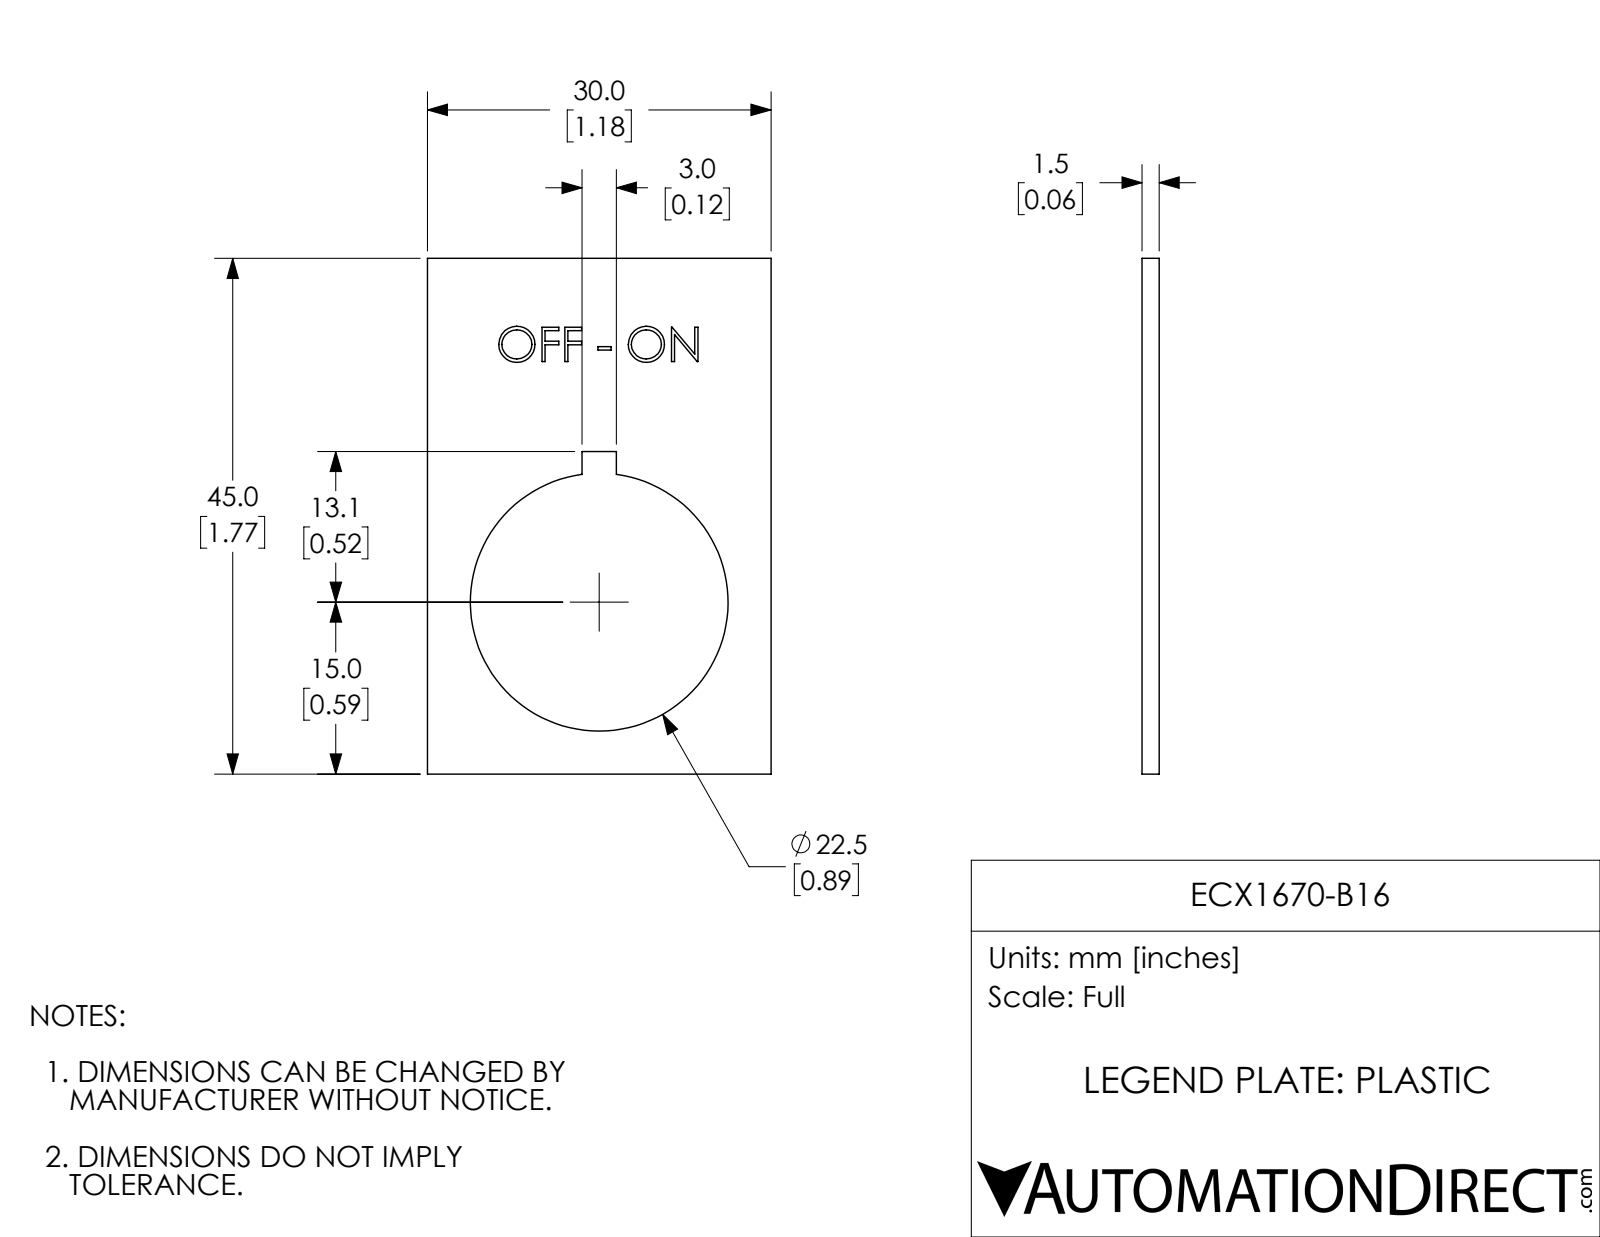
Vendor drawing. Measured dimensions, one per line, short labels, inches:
name: ECX1670-B16
written by: SolidWorks 2017 (AUTOMOTIVE_DESIGN)
unit: in
bodies: 1 solid, 70 faces (51 planar, 3 cylindrical, 16 other)
size: 1.772 × 1.181 × 0.059
volume: 0.087 in³; area: 3.46 in²
holes: 1× ⌀0.886
face distances: 0.059, 1.181, 1.772, 0.058, 0.531, 0.65, 1.108, 0.663, 0.118, 0.367
